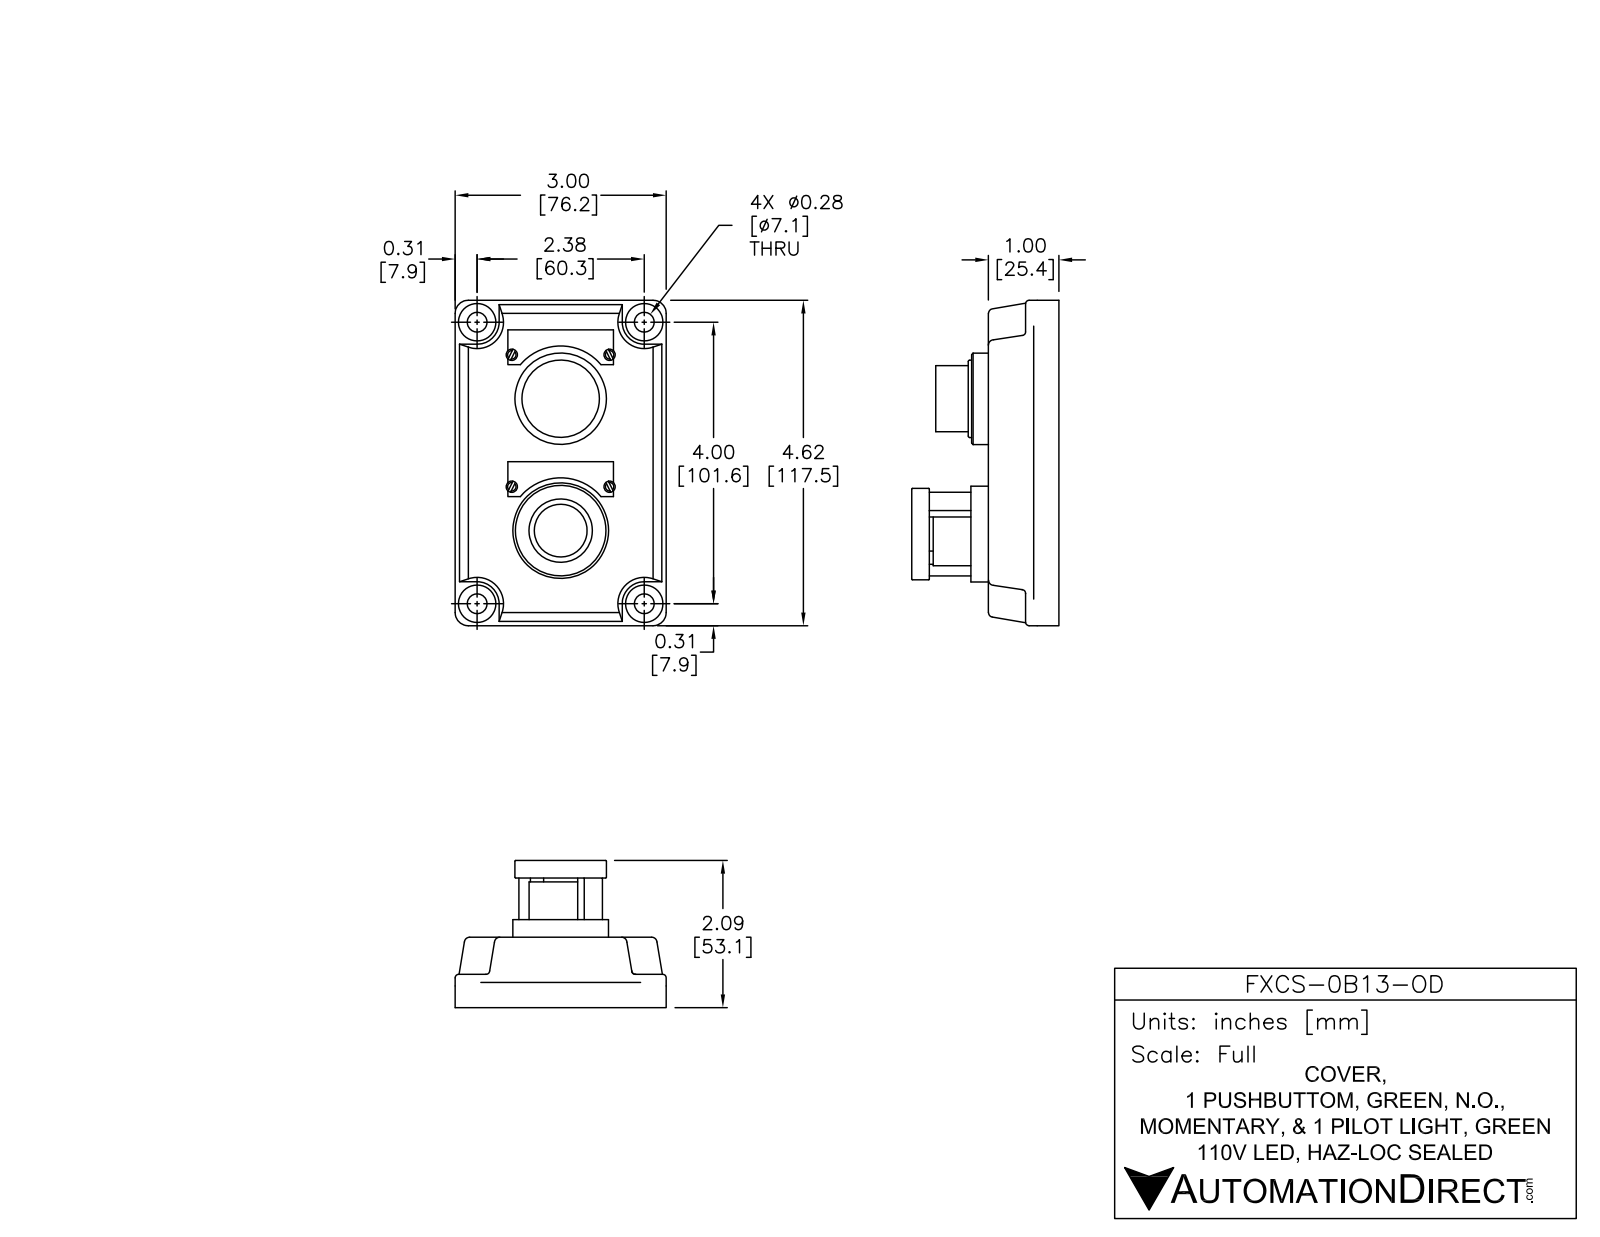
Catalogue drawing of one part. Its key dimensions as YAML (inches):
part_name: "FXCS-0B13-OD"
step_written_by: "SolidWorks 2015 (AUTOMOTIVE_DESIGN)"
units: inches
bodies: {solids: 1, faces: 748, planar: 310, cylindrical: 161, other: 277}
overall_size: [5.31, 4.989, 3.69]
volume: 49.84
surface_area: 107.7
round_holes:
  - {diameter: 0.16, count: 8}
  - {diameter: 0.198, count: 1}
  - {diameter: 0.94, count: 1}
  - {diameter: 1.1, count: 1}
round_bosses_or_shafts:
  - {diameter: 0.16, count: 8}
  - {diameter: 0.39, count: 4}
  - {diameter: 1.37, count: 1}
  - {diameter: 1.36, count: 1}
  - {diameter: 1.31, count: 1}
  - {diameter: 1.3, count: 1}
  - {diameter: 1, count: 1}
  - {diameter: 0.9, count: 1}
partial_cylinders:
  - {radius: 0.02, count: 22}
  - {radius: 0.05, count: 12}
  - {radius: 0.055, count: 4}
  - {radius: 0.06, count: 4}
  - {radius: 0.075, count: 4}
  - {radius: 0.185, count: 4}
  - {radius: 0.42, count: 4}
  - {radius: 0.653, count: 3}
face_to_face_distances: [3.39, 0.49, 2.9, 0.02, 3.69, 0.578, 3.111, 1.19, 0.7, 2.2]
hole_center_spacings: [0.25, 2.197, 0.5, 2.183, 2.239, 0.75, 1.169, 1.28]
